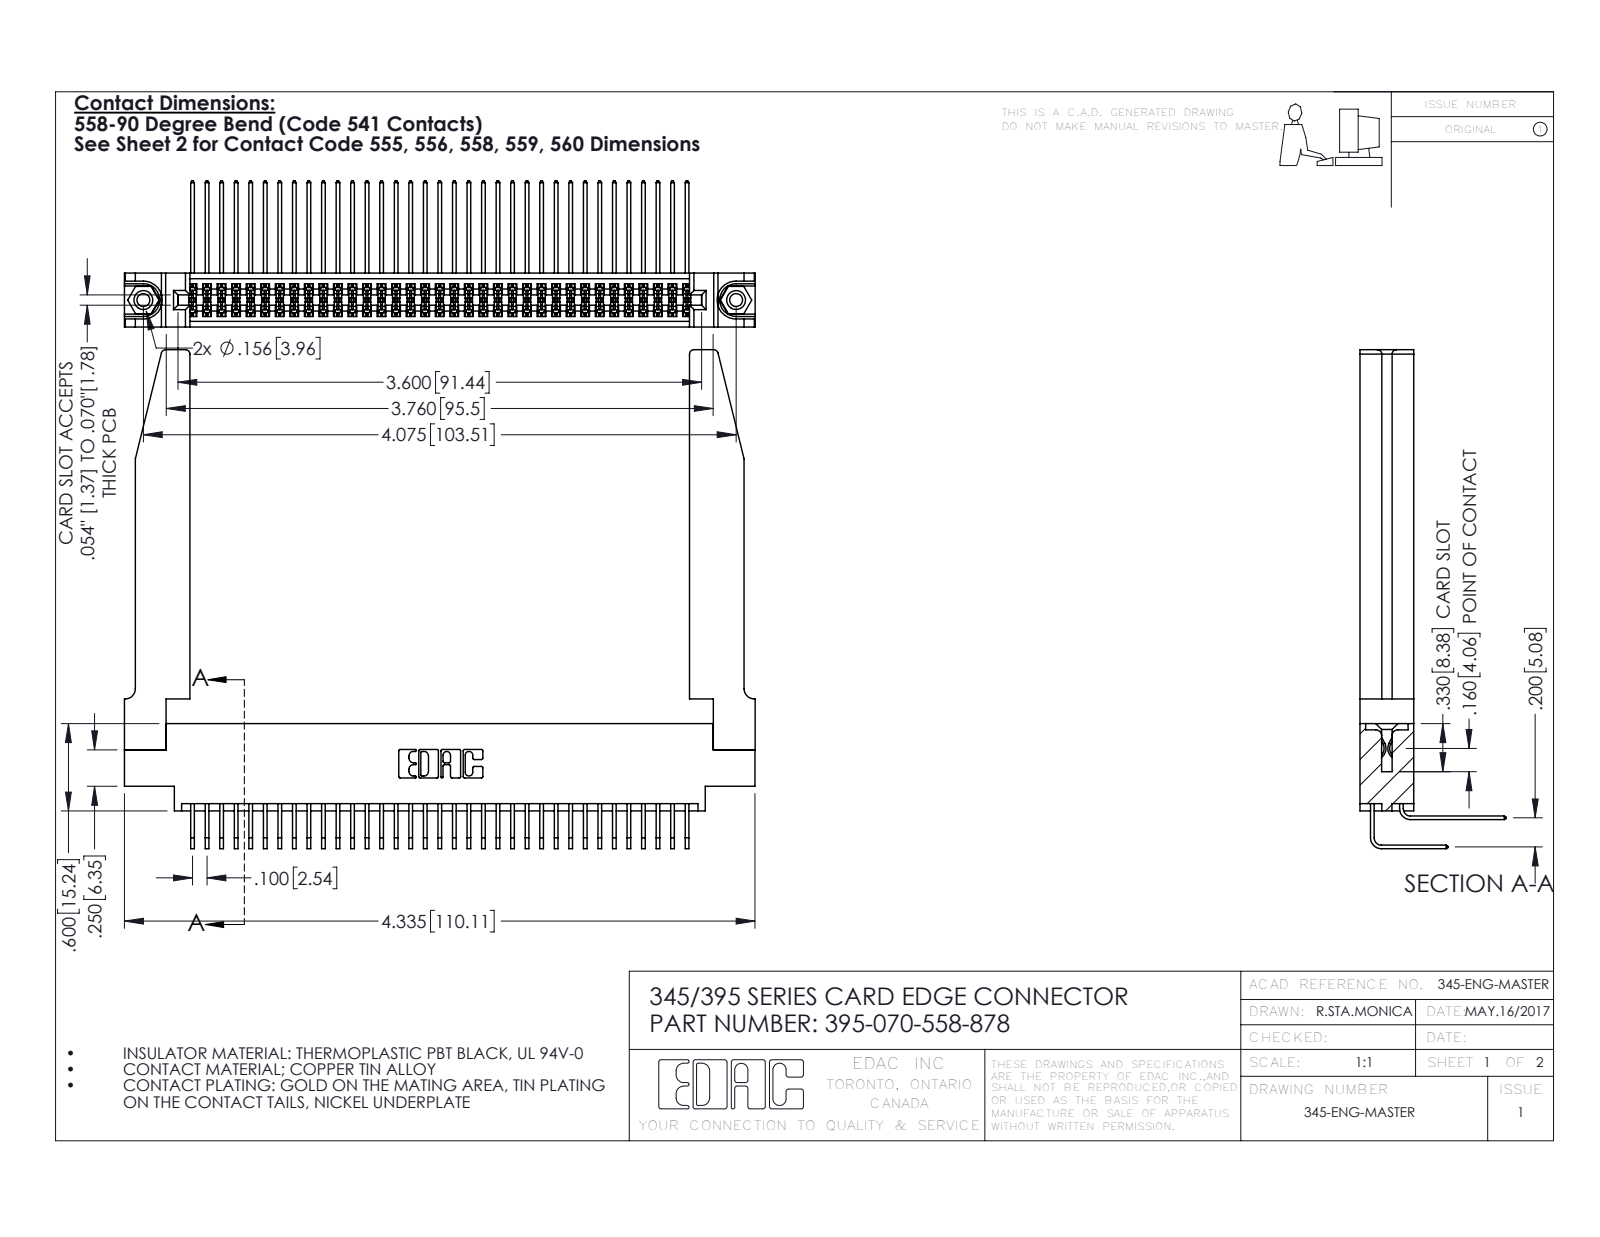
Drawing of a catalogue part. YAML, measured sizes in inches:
part_name: "345 Part_0.170 Offset - 0.156 Dia-TH; 345-220-078_345-220-078; 395-070-558-878; 345-292-001_558 Tail - 2 (+2 more)"
step_written_by: "SolidWorks 2016 (CONFIG_CONTROL_DESIGN)"
units: inches
bodies: {solids: 75, faces: 4004, planar: 2676, cylindrical: 1276, other: 52}
overall_size: [4.336, 3.429, 1.005]
volume: 1.141
surface_area: 38.58
round_holes:
  - {diameter: 0.089, count: 2}
  - {diameter: 0.125, count: 2}
  - {diameter: 0.156, count: 2}
  - {diameter: 0.064, count: 1}
round_bosses_or_shafts:
  - {diameter: 0.155, count: 2}
partial_cylinders:
  - {radius: 0.006, count: 106}
  - {radius: 0.01, count: 22}
  - {radius: 0.03, count: 8}
  - {radius: 0.007, count: 6}
  - {radius: 0.031, count: 6}
  - {radius: 0.026, count: 3}
  - {radius: 0.014, count: 2}
  - {radius: 0.019, count: 2}
face_to_face_distances: [0.37, 0.072, 0.298, 0.2, 0.098, 0.272, 0.025, 0.225, 0.175, 0.148]
hole_center_spacings: [0.27, 3.839, 4.075]
